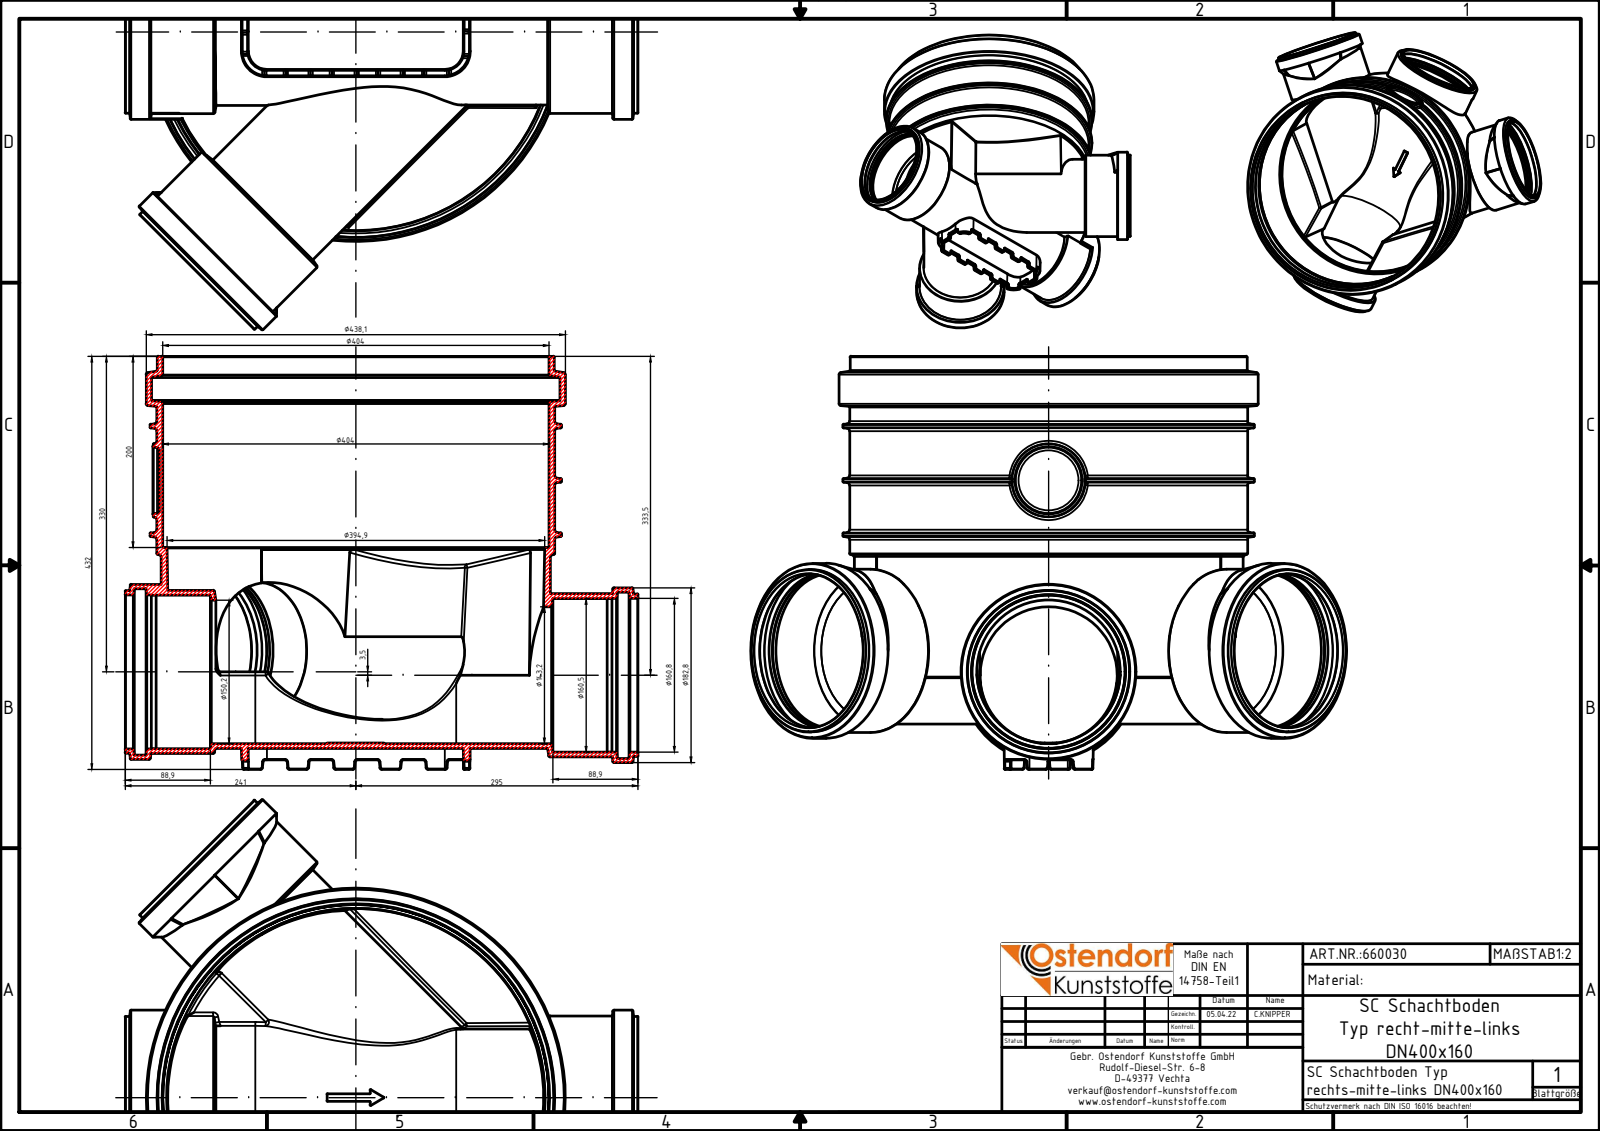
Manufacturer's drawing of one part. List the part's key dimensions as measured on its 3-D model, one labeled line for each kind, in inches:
Part name (STEP PRODUCT): 660030 SC Schachtboden Typ rechts-mitte-links DN400_160
STEP written by: Autodesk Inventor 2020 (AUTOMOTIVE_DESIGN)
Units: inches
Bodies: 1 solid, 703 faces (96 planar, 203 cylindrical, 404 other)
Overall size (bounding box): 24.527 × 21.102 × 17.008
Volume: 285.5 in³ · Surface area: 2 633 in²
Round holes (diameter × count): ⌀6.331 ×6, ⌀6.843 ×4, ⌀5.638 ×3, ⌀6.319 ×2, ⌀6.335 ×2, ⌀5.913 ×1, ⌀15.906 ×1, ⌀15.921 ×1, ⌀16.815 ×1
Round bosses / shafts (diameter × count): ⌀7.197 ×4, ⌀6.717 ×4, ⌀6.685 ×4, ⌀17.248 ×1, ⌀16.929 ×1, ⌀16.378 ×1, ⌀16.339 ×1, ⌀6.024 ×1
Partial cylindrical surfaces — rounded edges, fillets, slot ends (radius × count): R0.039 ×56, R0.079 ×48, R0.157 ×8, R0.02 ×7, R3.012 ×2, R3.36 ×1, R8.009 ×1
Main face-to-face distances: 3.385, 13.228, 5.354, 7.874, 0.236, 5.118, 12.992, 21.102, 9.133, 3.386
Hole centre spacings: 0.138
